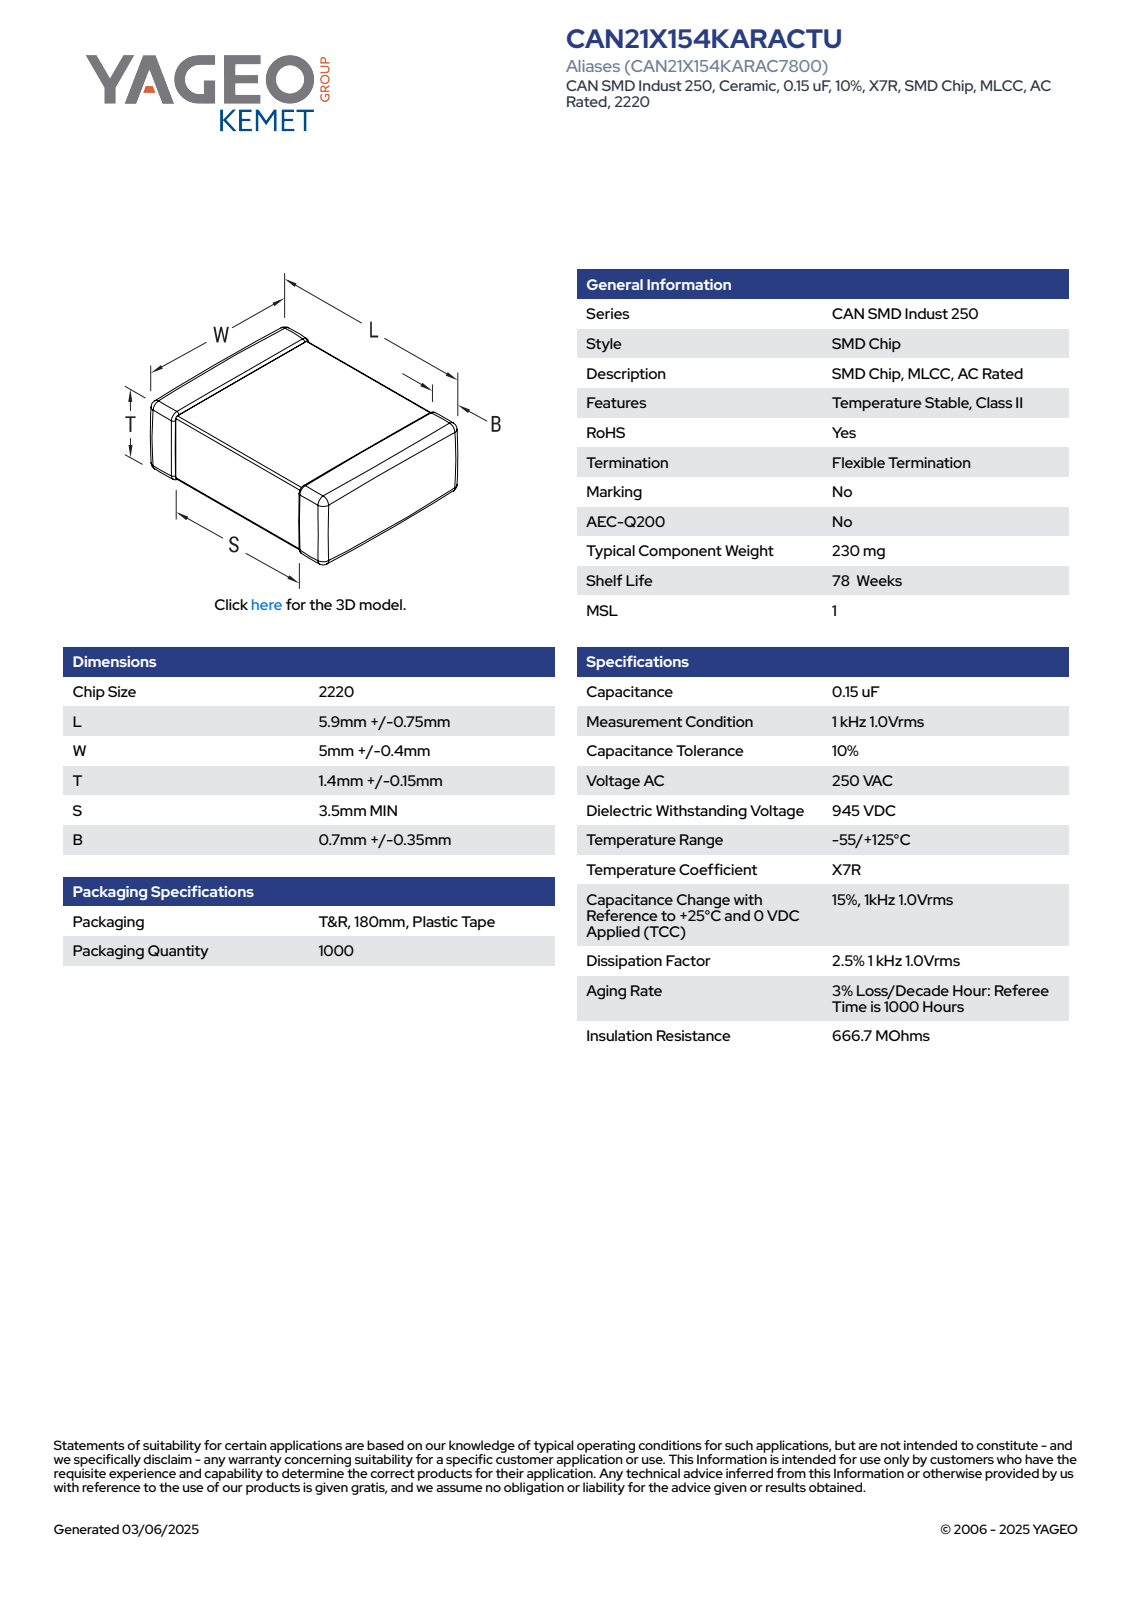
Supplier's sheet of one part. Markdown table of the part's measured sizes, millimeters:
| quantity | value |
| --- | --- |
| part name | CCS_CCSTD_2220_L6.65W5.4T1.55B0.7 |
| STEP written by | SolidWorks 2021 (AUTOMOTIVE_DESIGN) |
| units | millimeters |
| bodies | 4 solids, 121 faces (71 planar, 34 cylindrical, 16 other) |
| overall size | 6.65 × 5.4 × 1.55 |
| volume | 49 mm³ |
| surface area | 108 mm² |
| partial cylindrical surfaces (radius × count) | 0.11 × 24 |
| main face-to-face distances | 1.33, 1.44, 1.55, 6.65, 5.18, 5.29, 5.4, 2.8, 3.85, 3.59 |
